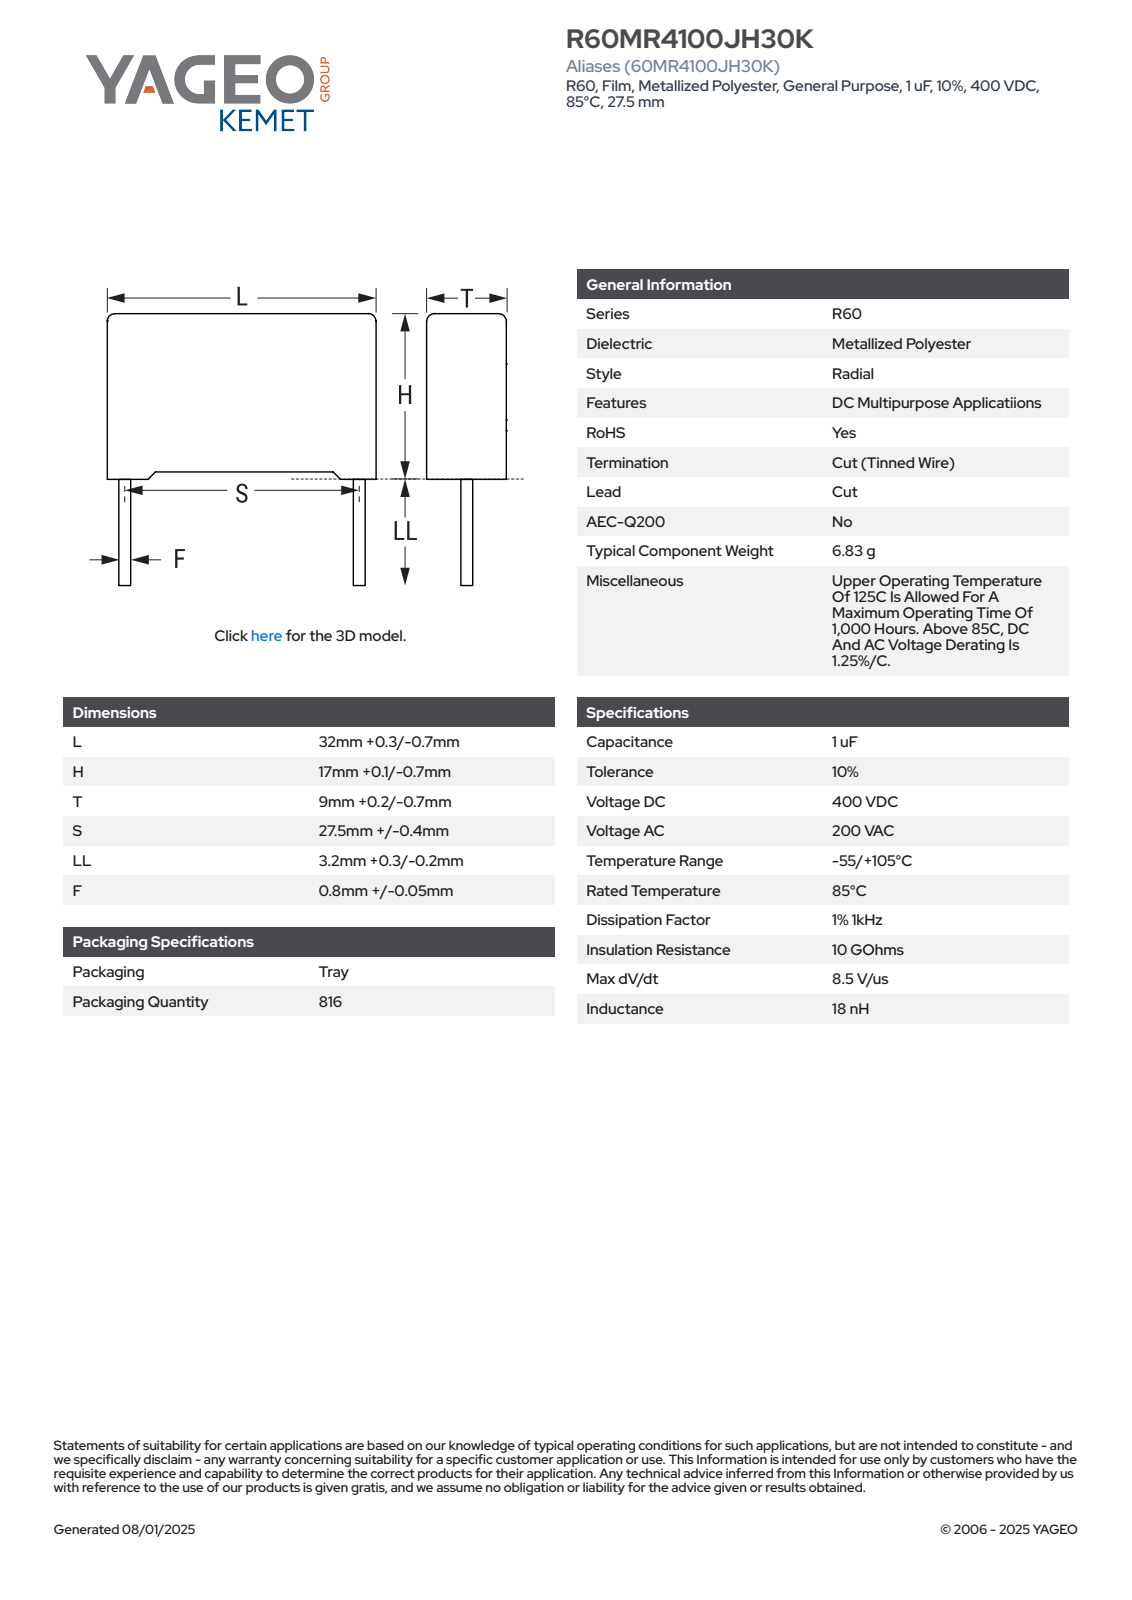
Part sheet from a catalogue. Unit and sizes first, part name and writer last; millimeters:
Units: millimetres
Overall size (bounding box): 32.3 × 20.6 × 9.21
Round bosses / shafts (diameter × count): ⌀0.85 ×2
Partial cylindrical surfaces — rounded edges, fillets, slot ends (radius × count): R0.5 ×4
Main face-to-face distances: 9.2, 16.35, 32.3, 16.51, 0.59, 0.75, 17.1, 1.08, 9.21, 8.12
Volume: 4 893 mm³ · Surface area: 2 097 mm²
Bodies: 4 solids, 85 faces (77 planar, 8 cylindrical, 0 other)
Part name (STEP PRODUCT): CFR_RB2_32X17X9_L32.3H17.1T9.2S27.5LL3.5F0.85
STEP written by: SolidWorks 2021 (AUTOMOTIVE_DESIGN)
